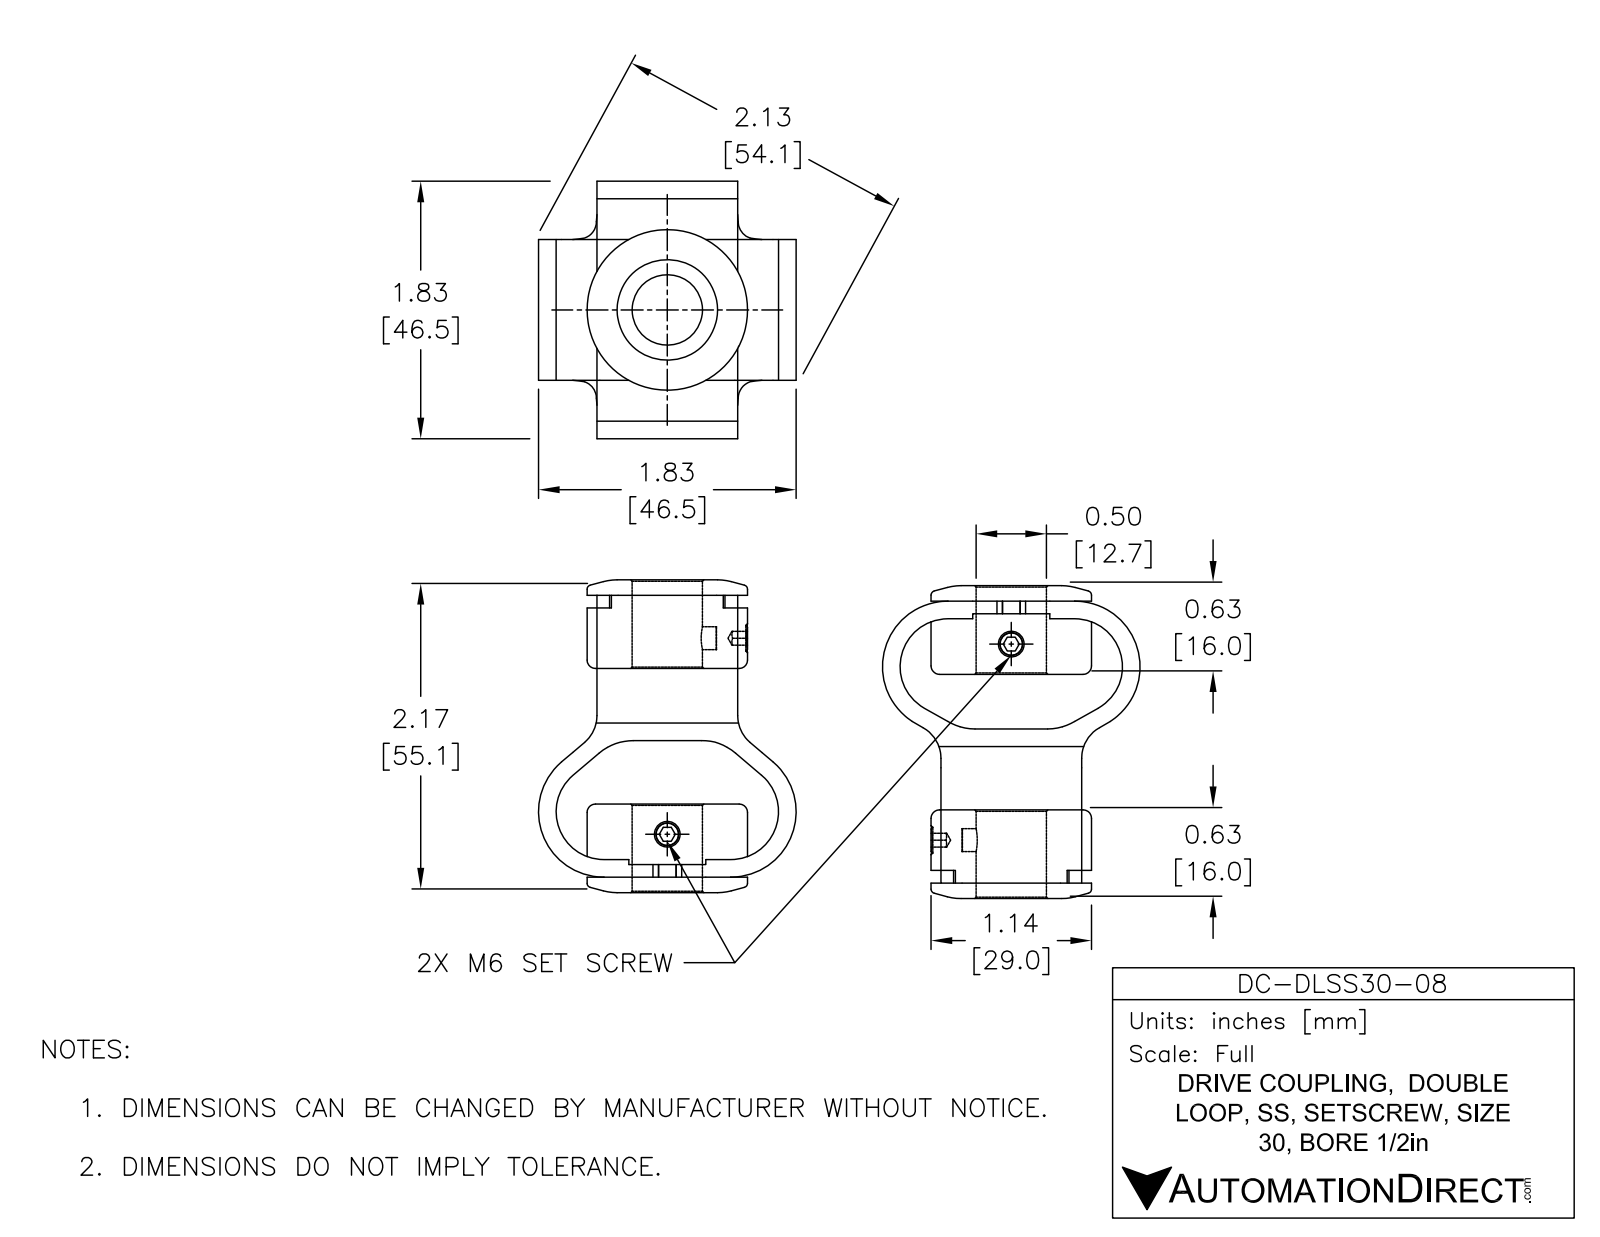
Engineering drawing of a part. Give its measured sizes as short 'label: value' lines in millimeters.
name: DC-DLSS30-08
written by: SolidWorks 2015 (AUTOMOTIVE_DESIGN)
unit: mm
bodies: 1 solid, 165 faces (88 planar, 37 cylindrical, 40 other)
size: 56.46 × 46.48 × 46.48
volume: 28 285 mm³; area: 15 053 mm²
holes: 2× ⌀5.26, 1× ⌀12.7
bosses: 1× ⌀28.96
rounds: 4× R8.64, 4× R9.53, 4× R11.81, 1× R10.41
face distances: 25.4, 24.46, 3.17, 14.61, 9.85, 11.44, 13.02, 16, 40.46, 24.64
